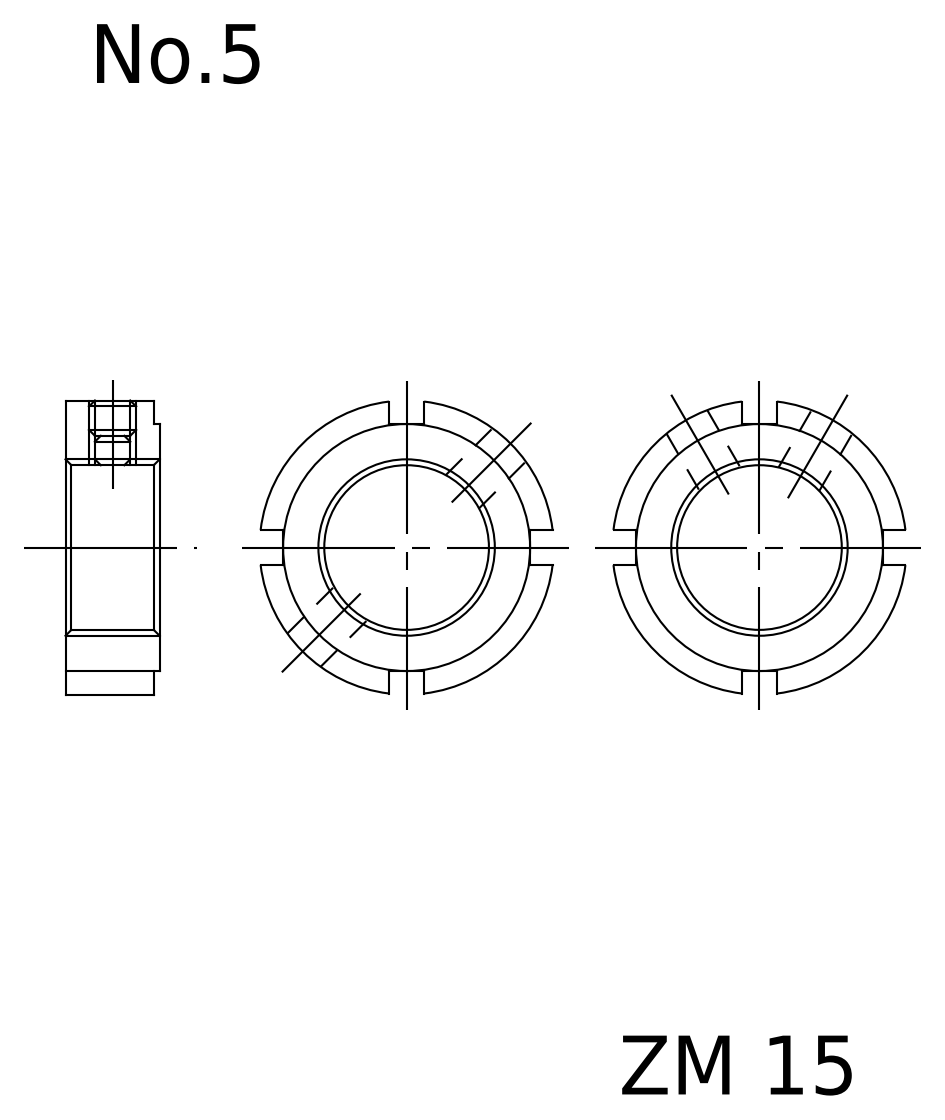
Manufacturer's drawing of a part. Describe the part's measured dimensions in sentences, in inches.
The part is named "FKD ZM 15". Its 3-D file was written by "Autodesk Inventor 2011 (AUTOMOTIVE_DESIGN)". It is 1 solid with 26 faces: 18 planar, 8 cylindrical and 0 other. Overall it measures 0.977 by 0.977 by 0.315 inches. Its volume is 0.133 cubic inches and its surface area 2.734 square inches. Round holes: 2 of diameter 0.128, 1 of diameter 0.591. Round bosses or shafts: 1 of diameter 0.984, 1 of diameter 0.827. The main face-to-face distances are 0.315, 0.02, 0.295, 0.354, 0.472, 0.118, 0.827.
